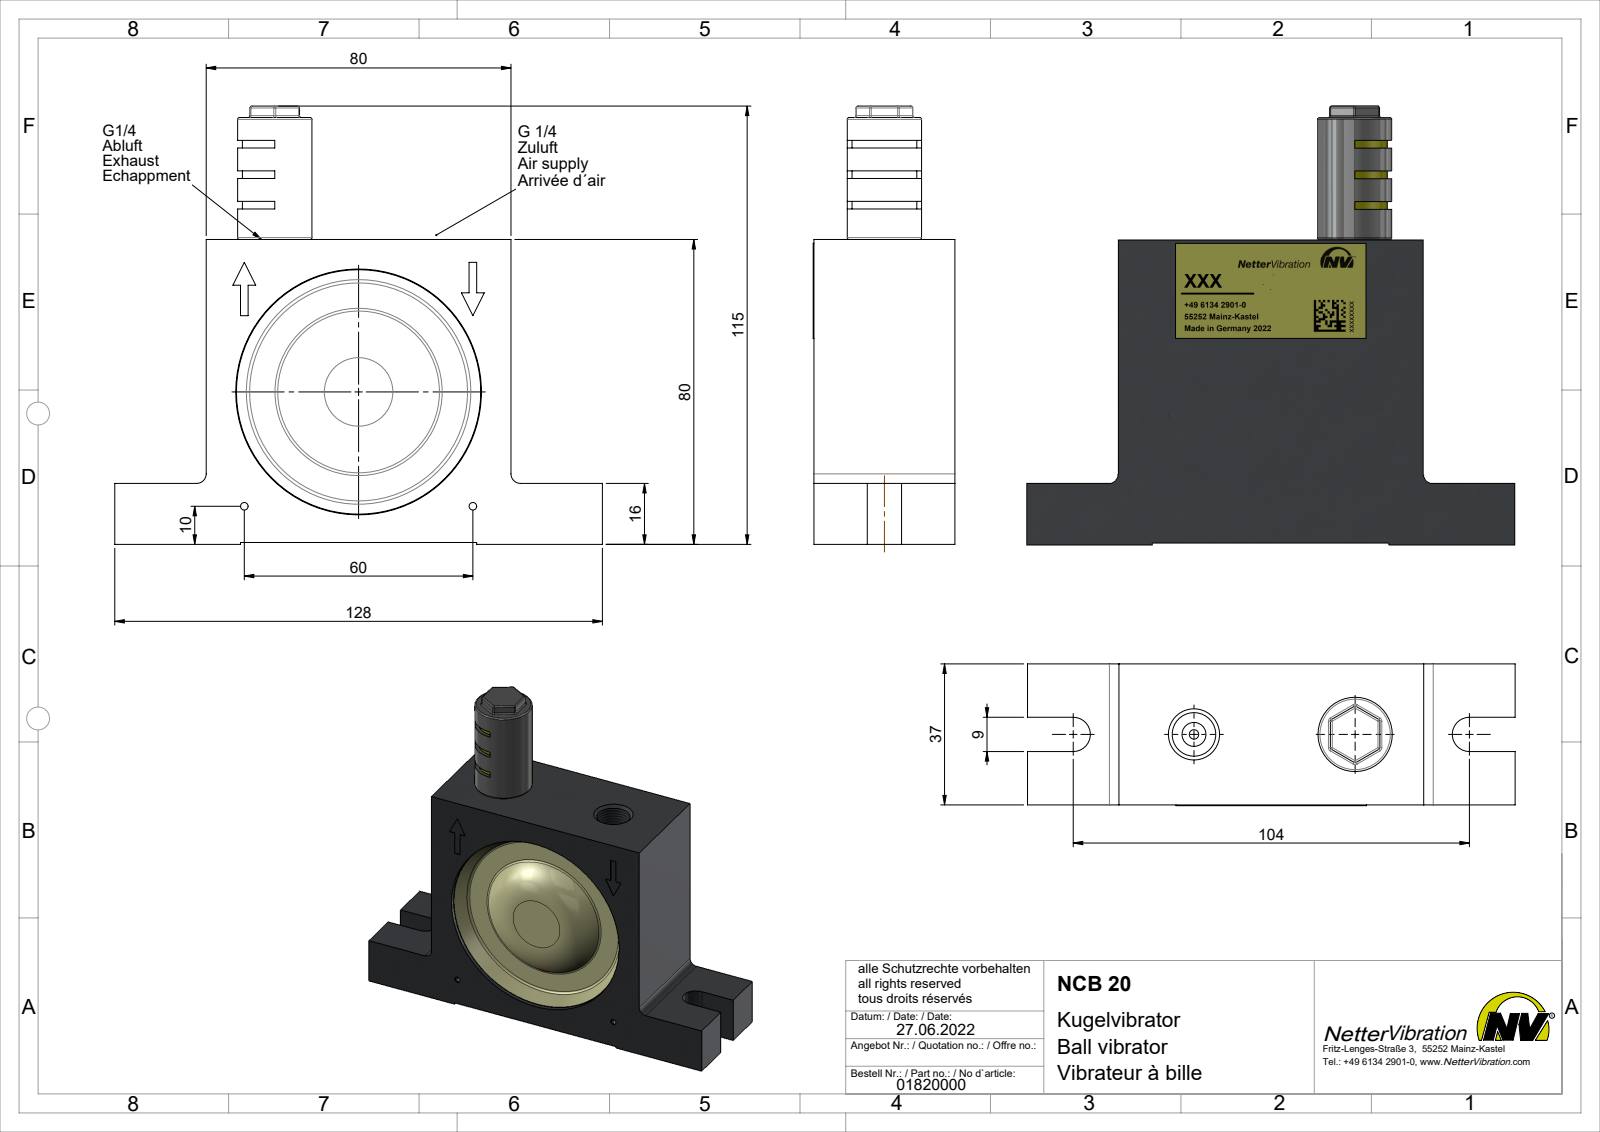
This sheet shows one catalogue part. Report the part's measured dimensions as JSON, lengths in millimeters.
{"part_name": "NCB 20 Kugelvibrator # 01820000", "step_written_by": "SolidWorks 2015 (AUTOMOTIVE_DESIGN)", "units": "millimeters", "bodies": {"solids": 3, "faces": 232, "planar": 104, "cylindrical": 54, "other": 74}, "overall_size": [128, 115, 37], "volume_mm3": 186852, "surface_area_mm2": 47803, "round_holes": [[2, 2], [11.45, 2], [2.5, 1], [4.1, 1], [10, 1], [55, 1], [62, 1], [64.5, 1]], "round_bosses_or_shafts": [[19.5, 1], [13.16, 1]], "partial_cylinders_radius": [[0.5, 18], [2.5, 2], [4.5, 2], [8.5, 1]], "face_to_face_distances": [80, 37, 79.5, 0.5, 6.85, 7.15, 16, 15.5, 64, 8.5], "hole_center_spacings": [42.43, 65.92, 28.7, 42.3, 60]}
